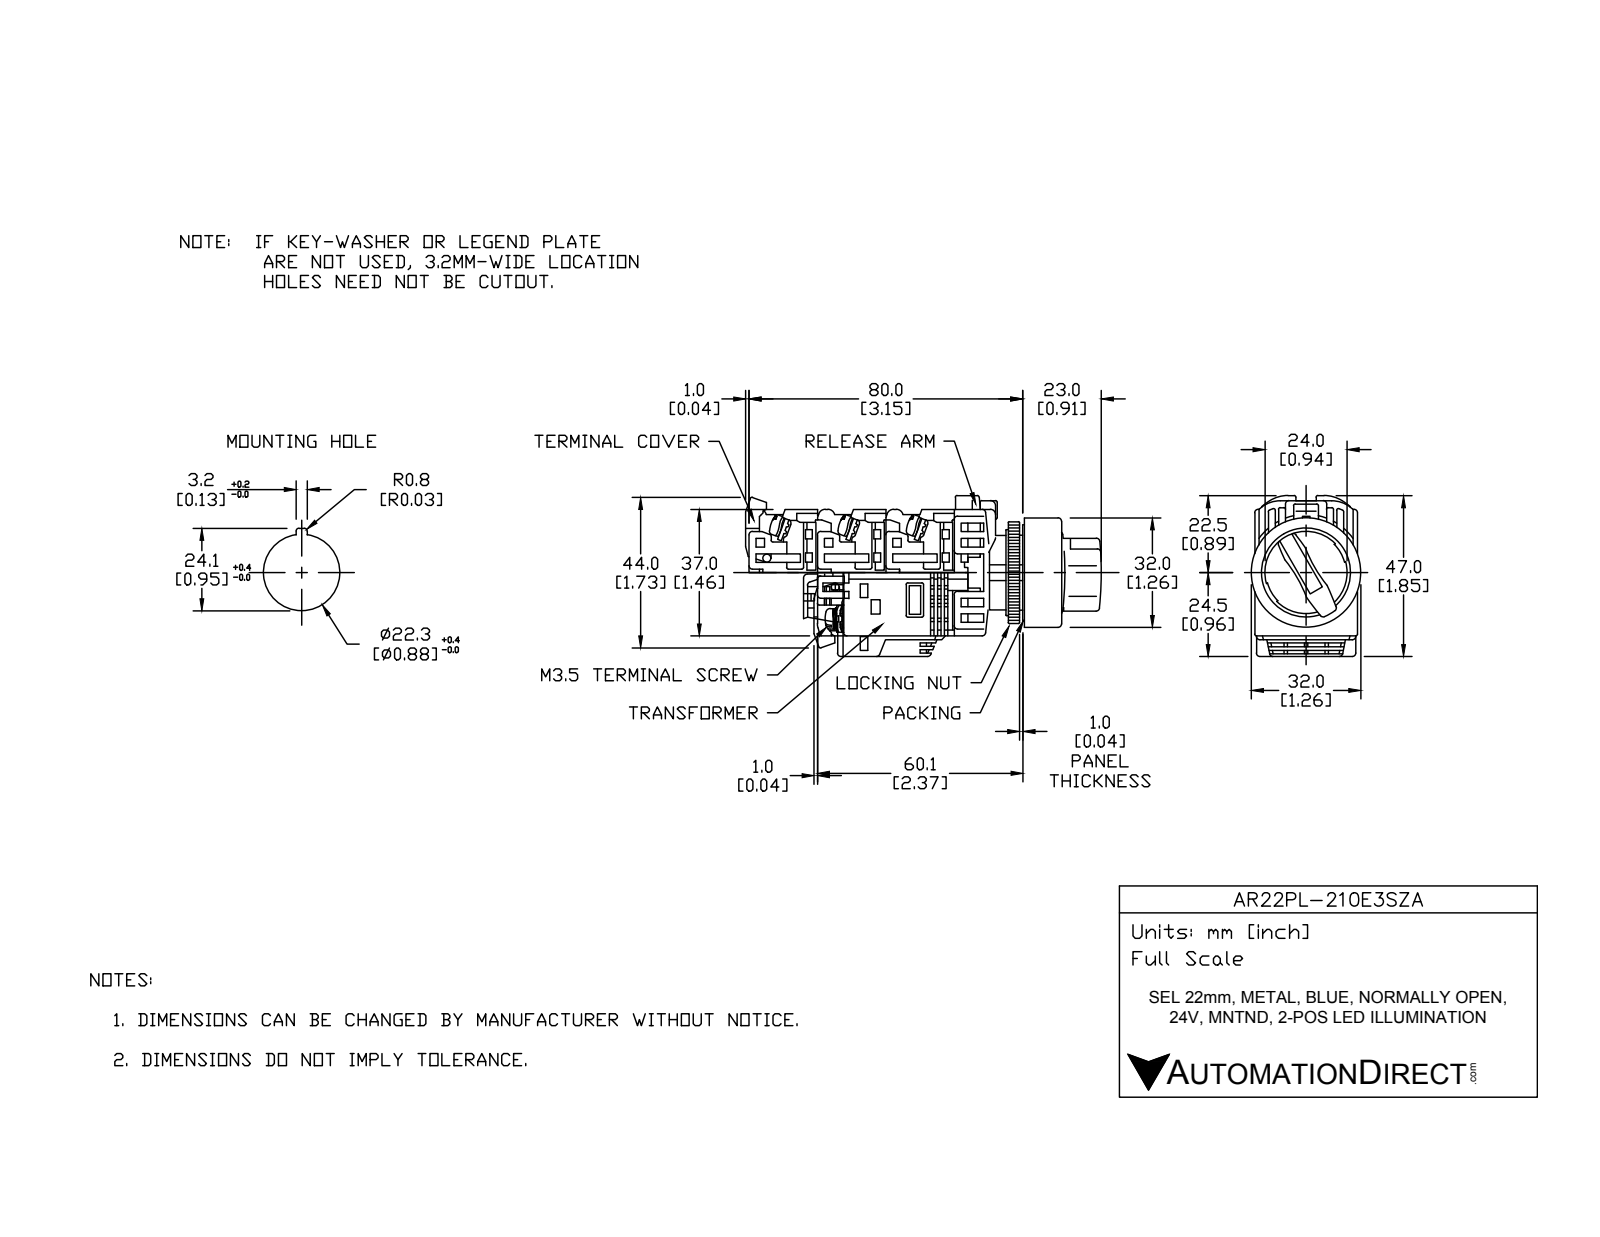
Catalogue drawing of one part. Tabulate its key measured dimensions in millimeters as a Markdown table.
| quantity | value |
| --- | --- |
| part name | AR22PL-210E3SZA |
| STEP written by | SolidWorks 2017 (AUTOMOTIVE_DESIGN) |
| units | millimeters |
| bodies | 18 solids, 462 faces (317 planar, 118 cylindrical, 27 other) |
| overall size | 64.5 × 43.81 × 32 |
| volume | 38 531 mm³ |
| surface area | 24 831 mm² |
| round holes (diameter × count) | 21.8 × 1, 22 × 1, 25 × 1, 31 × 1 |
| round bosses / shafts (diameter × count) | 5 × 4, 32 × 1, 30.5 × 1, 29.8 × 1, 24 × 1, 21.75 × 1, 17 × 1 |
| partial cylindrical surfaces (radius × count) | 0.5 × 39, 1.75 × 8, 1 × 6, 5 × 4, 4 × 2, 12 × 1, 16.59 × 1, 17.59 × 1 |
| main face-to-face distances | 1, 18, 3, 28.5, 48.5, 20, 29, 0.5, 2, 31 |
